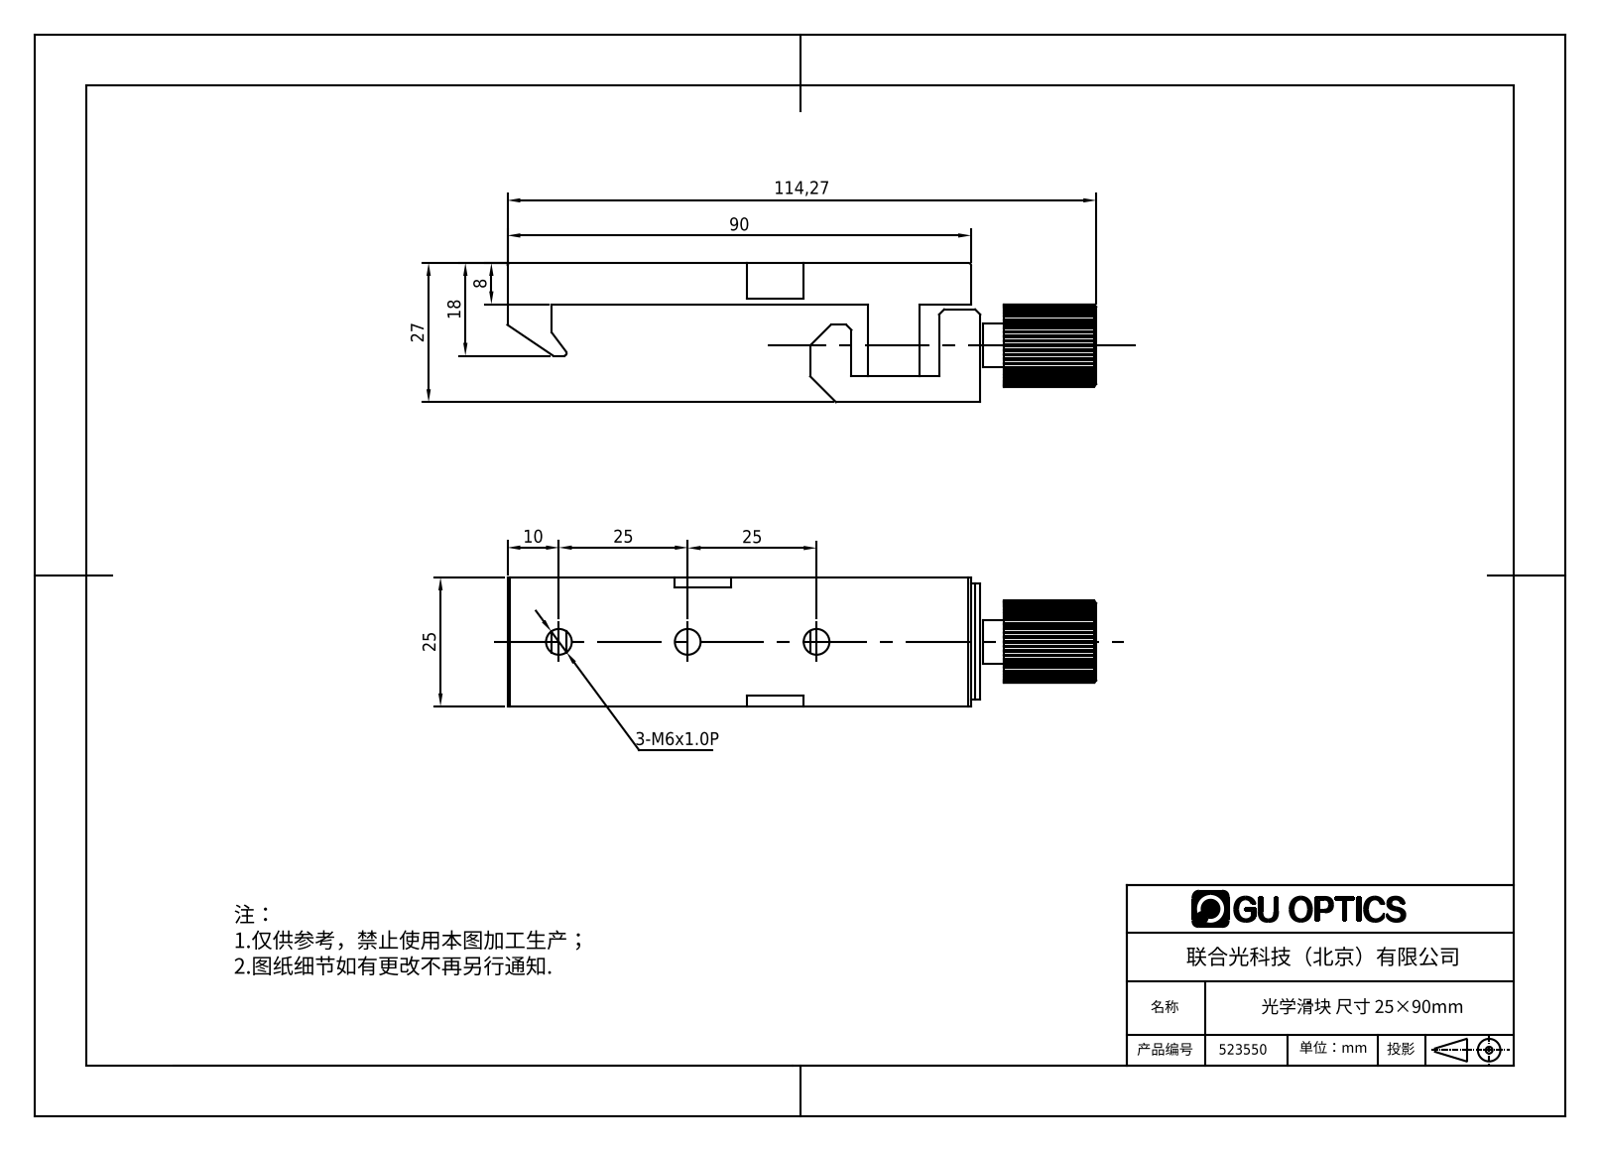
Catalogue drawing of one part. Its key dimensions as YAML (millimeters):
part_name: "CRL-1"
step_written_by: "SolidWorks 2012 (CONFIG_CONTROL_DESIGN)"
units: millimeters
bodies: {solids: 0, faces: 213, planar: 149, cylindrical: 63, other: 1}
overall_size: [114.27, 27, 25]
round_holes:
  - {diameter: 5, count: 3}
round_bosses_or_shafts:
  - {diameter: 8.5, count: 1}
partial_cylinders:
  - {radius: 0.5, count: 3}
  - {radius: 8, count: 1}
face_to_face_distances: [8, 25, 1.25, 23.75, 14, 10, 22, 5, 19, 27]
hole_center_spacings: [25, 50]
